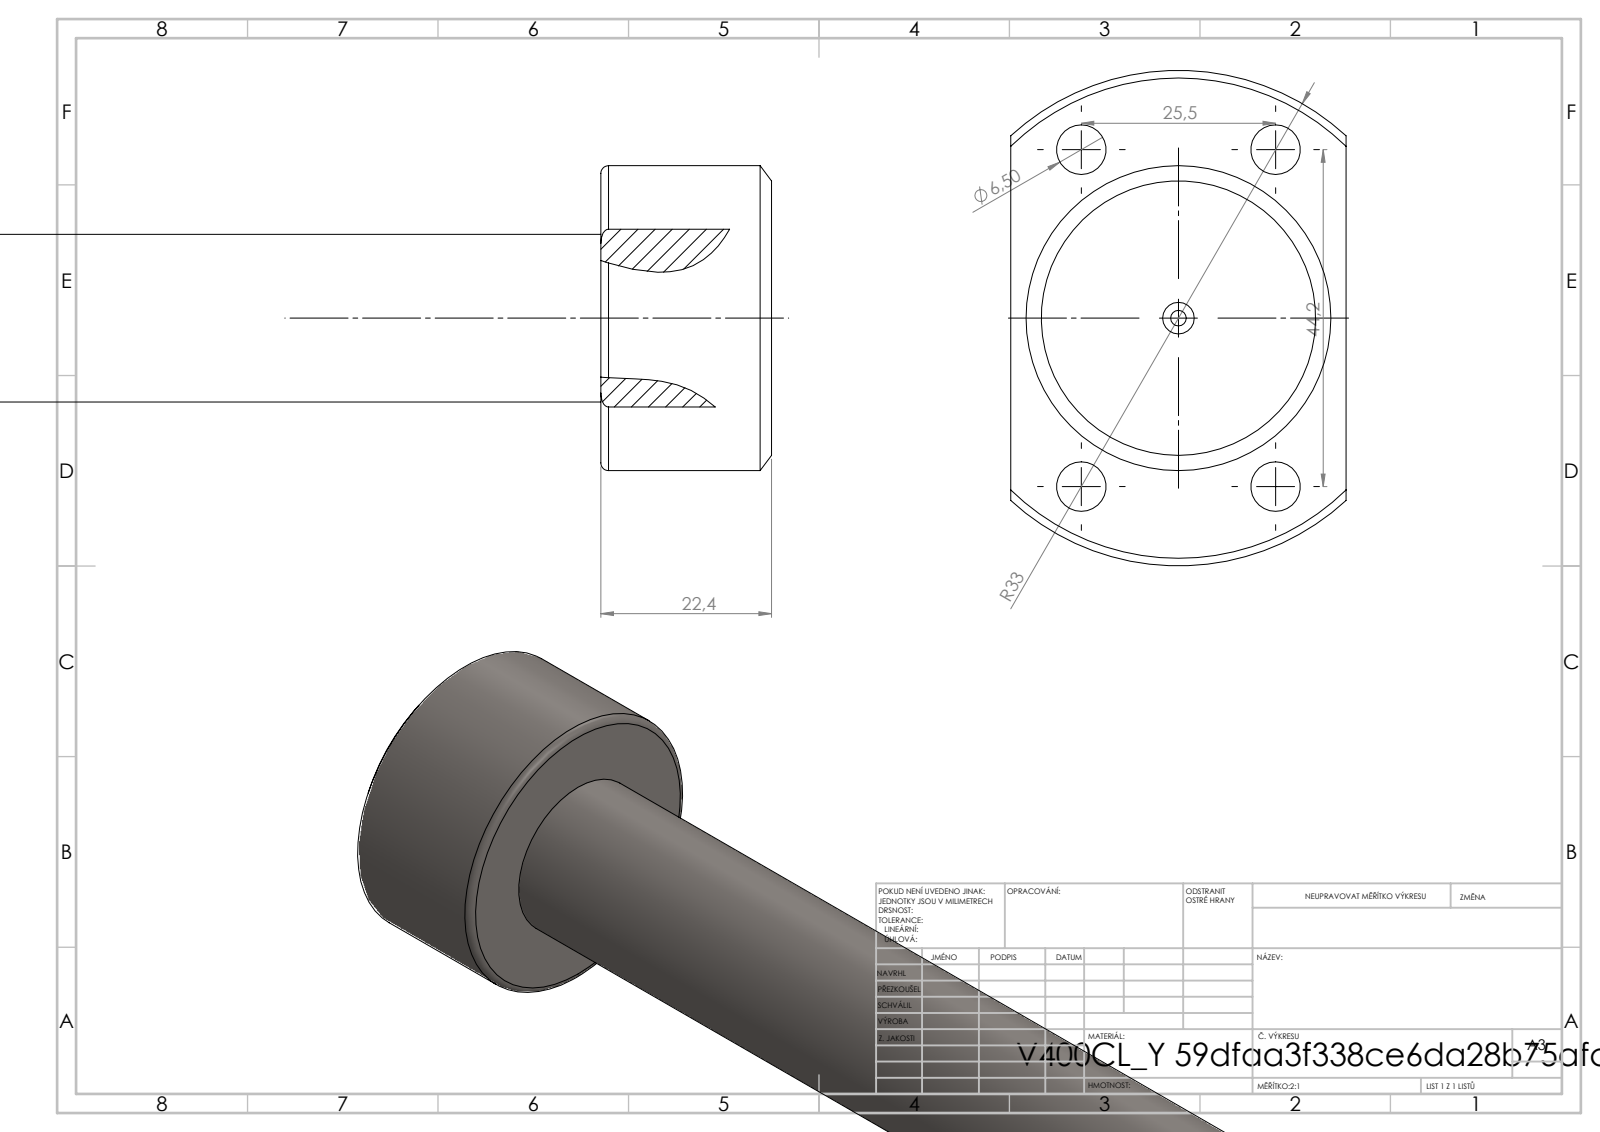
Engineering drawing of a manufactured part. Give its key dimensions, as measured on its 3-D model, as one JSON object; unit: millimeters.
{"part_name": "V400CL_PC_Y; V400CL_VC_X", "step_written_by": "SolidWorks 2019 (CONFIG_CONTROL_DESIGN)", "units": "millimeters", "bodies": {"solids": 2, "faces": 103, "planar": 26, "cylindrical": 47, "other": 30}, "overall_size": [263, 65, 44], "volume_mm3": 161549, "surface_area_mm2": 34965, "round_holes": [[6.5, 4], [10.5, 4], [2.05, 1], [5, 1], [6, 1], [22, 1], [26.5, 1]], "round_bosses_or_shafts": [[40, 1], [39, 1]], "partial_cylinders_radius": [[10.75, 1], [32.5, 1]], "face_to_face_distances": [14, 242.95, 256.95, 22.4, 220.55, 234.55, 225.45, 203.05, 17.5, 31.5], "hole_center_spacings": [25.51, 25.5, 44.2, 51.03]}
